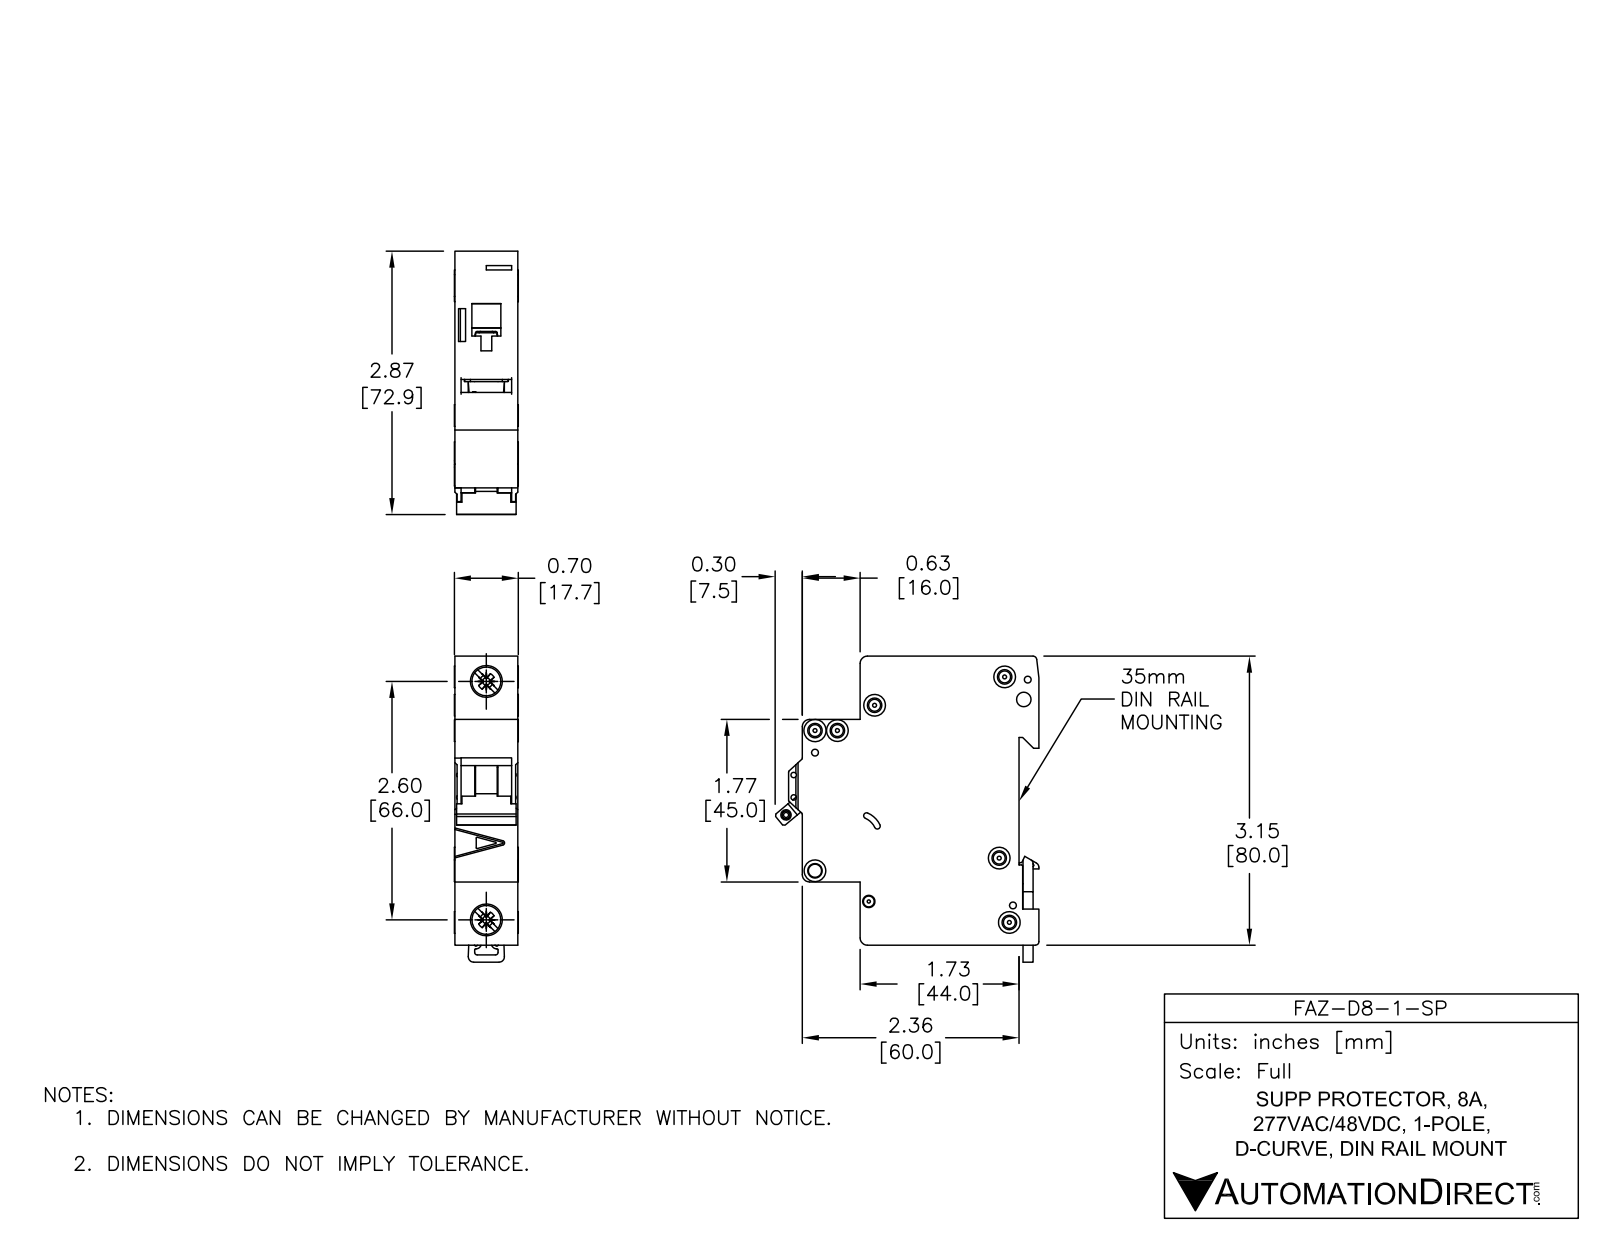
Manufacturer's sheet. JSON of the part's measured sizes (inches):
{"part_name": "FAZ-D8-1-SP", "step_written_by": "SolidWorks 2014 (AUTOMOTIVE_DESIGN)", "units": "inches", "bodies": {"solids": 5, "faces": 558, "planar": 235, "cylindrical": 202, "other": 121}, "overall_size": [3.338, 2.876, 0.697], "volume_in3": 4.573, "surface_area_in2": 30.29, "round_holes": [[0.142, 6], [0.075, 3], [0.043, 2], [0.059, 2], [0.157, 2], [0.281, 2], [0.085, 1], [0.087, 1], [0.1, 1], [0.13, 1], [0.134, 1]], "round_bosses_or_shafts": [[0.236, 4], [0.323, 2], [0.098, 1]], "partial_cylinders_radius": [[0.01, 30], [0.02, 13], [0.079, 8], [0.008, 5], [0.039, 4], [0.031, 2], [0.118, 2], [0.059, 1]], "face_to_face_distances": [0.689, 3.129, 0.217, 1.949, 1.732, 2.579, 2.362, 0.63, 0.069, 0.62], "hole_center_spacings": [0.244, 0.537, 0.189, 0.204, 0.221, 0.24, 0.254, 0.322]}
